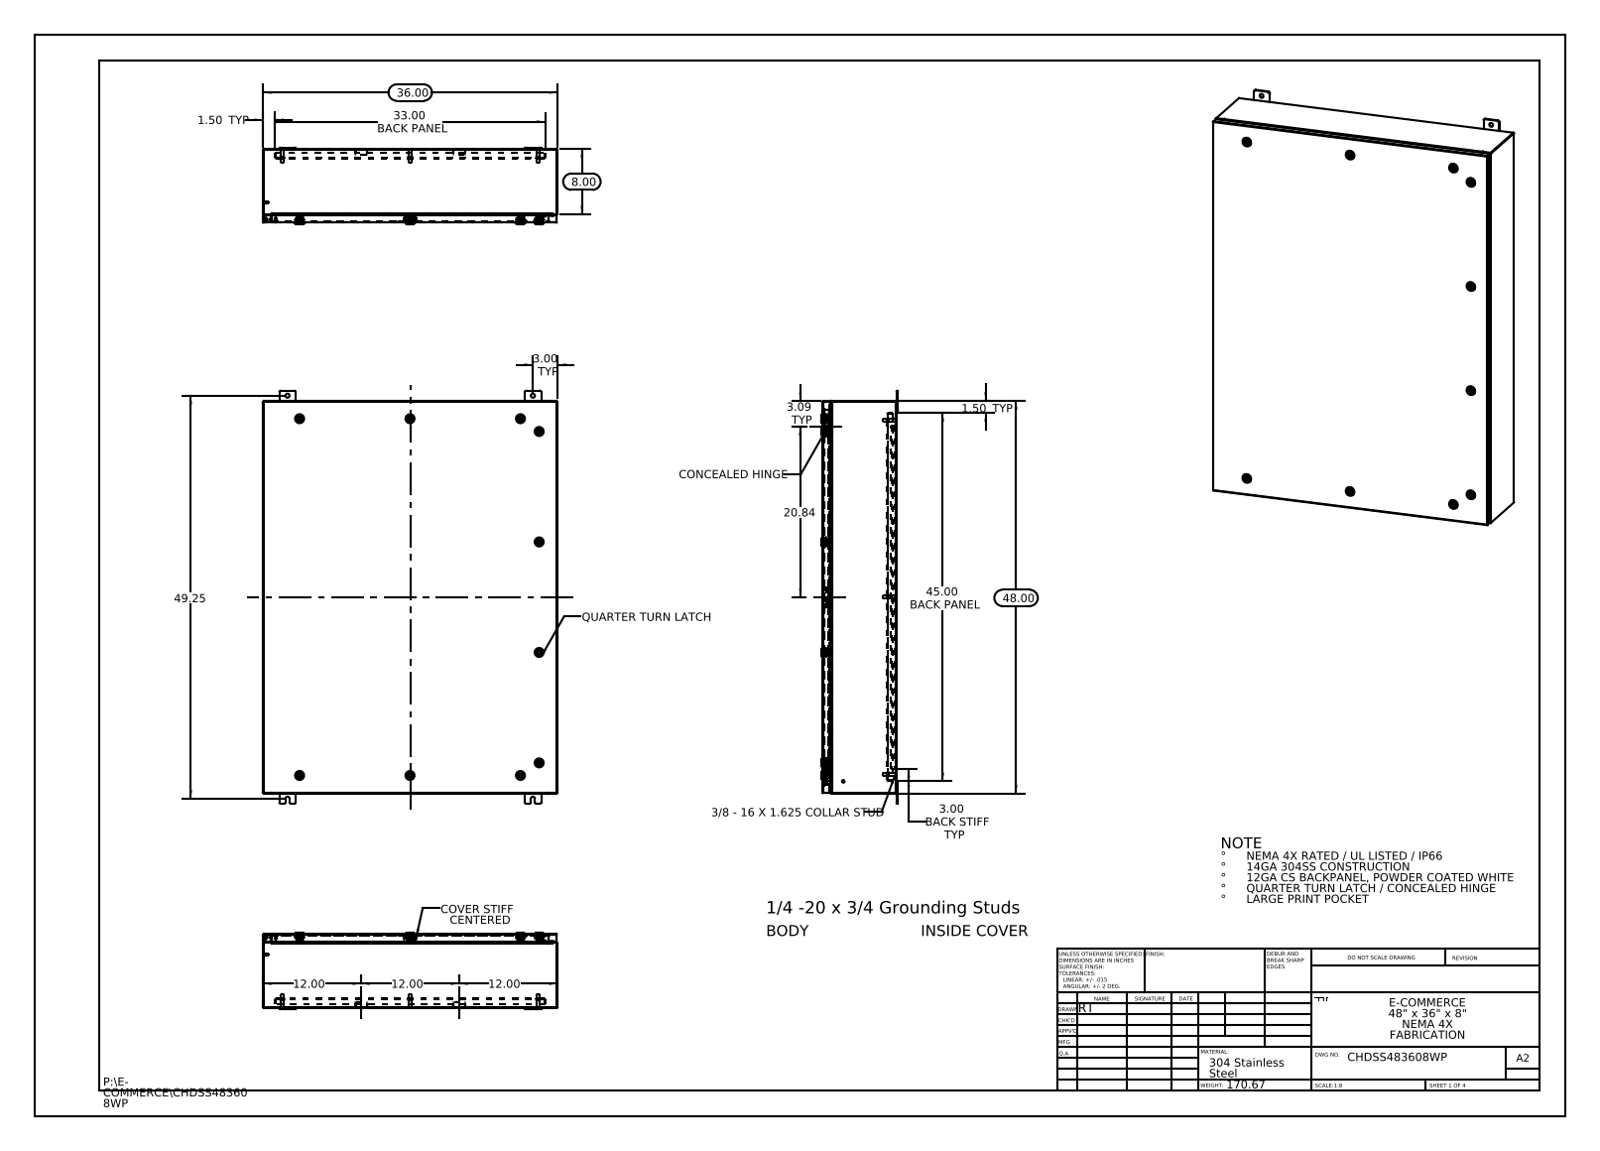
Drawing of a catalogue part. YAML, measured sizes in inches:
part_name: "CHDSS483608WP Mounting Studs; Washer-221320-IB-Industrilas_Washer-221320-IB-Industrilas; Housing-211301-IB-Industrilas_Housing-211301-IB-Industrilas; CHDSS483608WP Body (+8 more)"
step_written_by: "SolidWorks 2013 (CONFIG_CONTROL_DESIGN)"
units: inches
bodies: {solids: 94, faces: 9060, planar: 2626, cylindrical: 2826, other: 3608}
overall_size: [50.5, 36, 9.356]
volume: 603.3
surface_area: 14901
round_holes:
  - {diameter: 0.5, count: 12}
  - {diameter: 0.197, count: 10}
  - {diameter: 0.394, count: 10}
  - {diameter: 0.4, count: 10}
  - {diameter: 0.63, count: 10}
  - {diameter: 0.787, count: 10}
  - {diameter: 0.136, count: 6}
  - {diameter: 0.25, count: 6}
  - {diameter: 0.211, count: 1}
round_bosses_or_shafts:
  - {diameter: 0.236, count: 12}
  - {diameter: 1.102, count: 10}
  - {diameter: 0.78, count: 10}
  - {diameter: 0.626, count: 10}
  - {diameter: 0.61, count: 10}
  - {diameter: 0.531, count: 10}
  - {diameter: 0.392, count: 10}
  - {diameter: 0.114, count: 10}
partial_cylinders:
  - {radius: 0.006, count: 330}
  - {radius: 0.118, count: 330}
  - {radius: 0.028, count: 120}
  - {radius: 0.02, count: 40}
  - {radius: 0.197, count: 40}
  - {radius: 0.013, count: 34}
  - {radius: 0.088, count: 30}
  - {radius: 0.19, count: 24}
face_to_face_distances: [0.075, 0.074, 8.861, 8.936, 9.01, 8.935, 0.104, 1, 1.075, 7.861]
hole_center_spacings: [13.5, 20, 20.123, 21.625, 27, 38.003, 45.642, 45.986]
